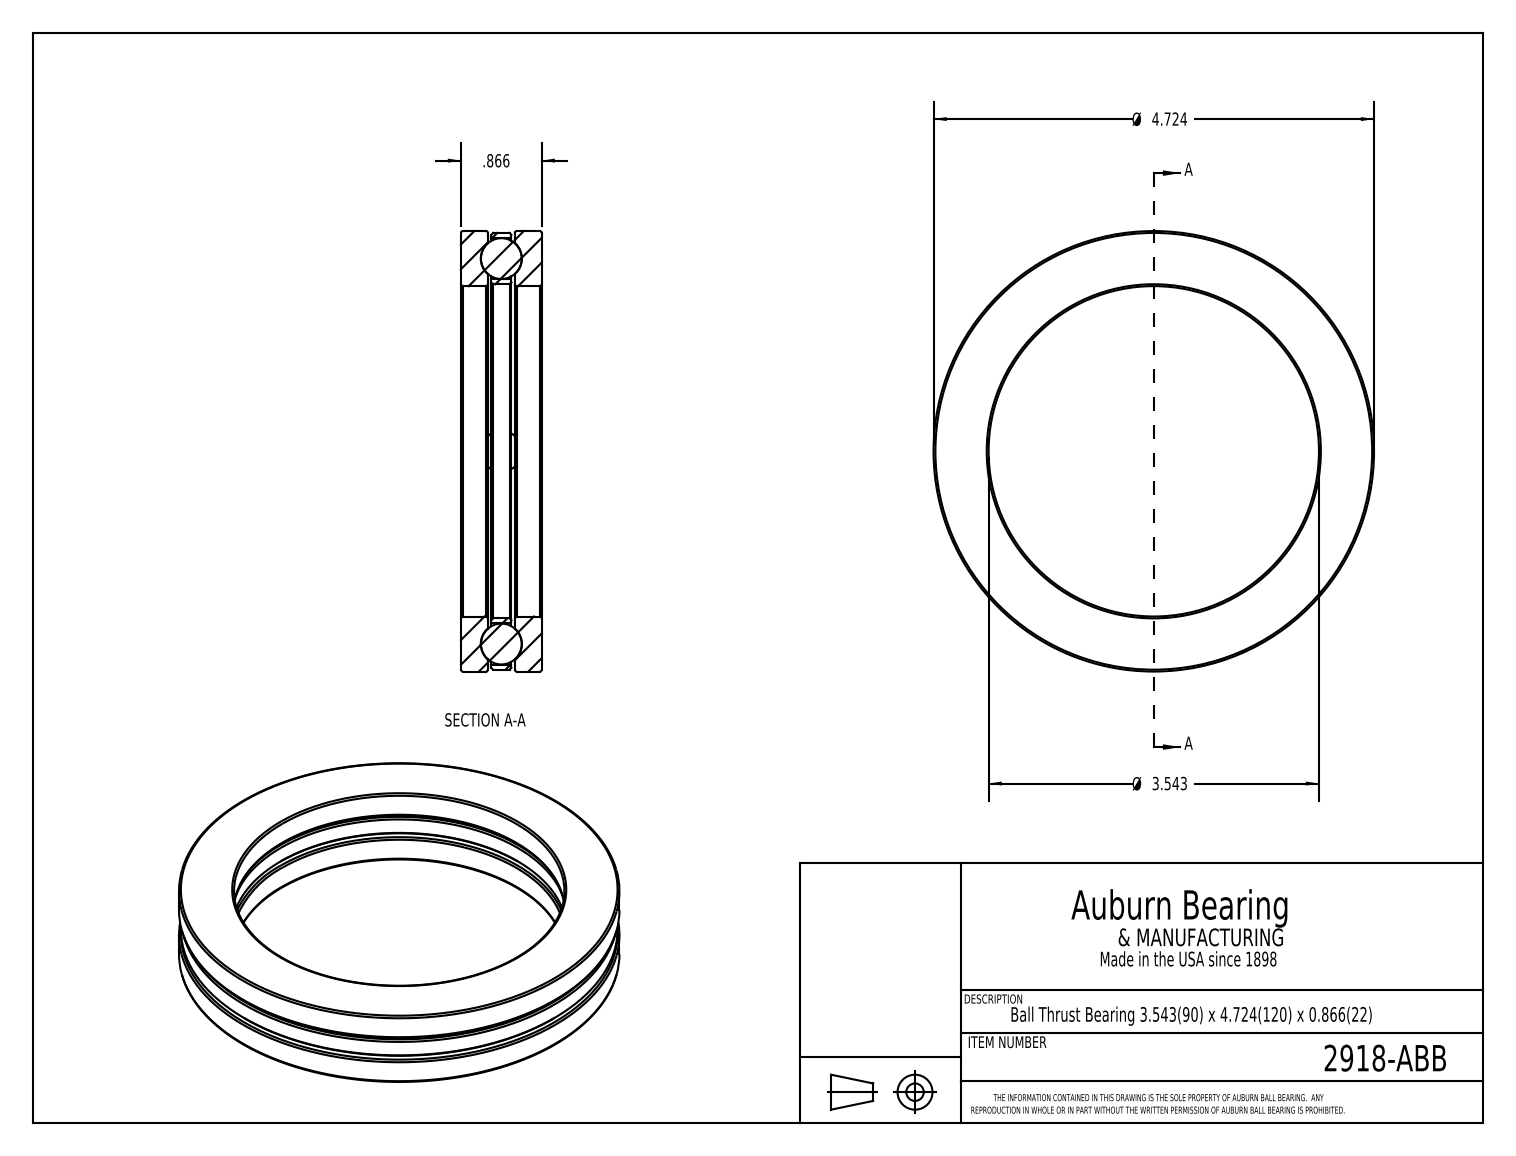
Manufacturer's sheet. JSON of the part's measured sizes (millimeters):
{"part_name": "2918-ABB", "step_written_by": "SolidWorks 2017 (CONFIG_CONTROL_DESIGN)", "units": "millimeters", "bodies": {"solids": 7, "faces": 36, "planar": 8, "cylindrical": 10, "other": 18}, "overall_size": [120, 120, 22], "volume_mm3": 90980, "surface_area_mm2": 43600, "round_holes": [[11.4, 4], [90, 1], [91, 1]], "round_bosses_or_shafts": [[120, 1], [119, 1]], "face_to_face_distances": [8.3, 13.7, 22, 5.5, 7.3, 14.7, 0.9, 6.4, 7.3], "hole_center_spacings": [52.5, 74.2, 105]}
